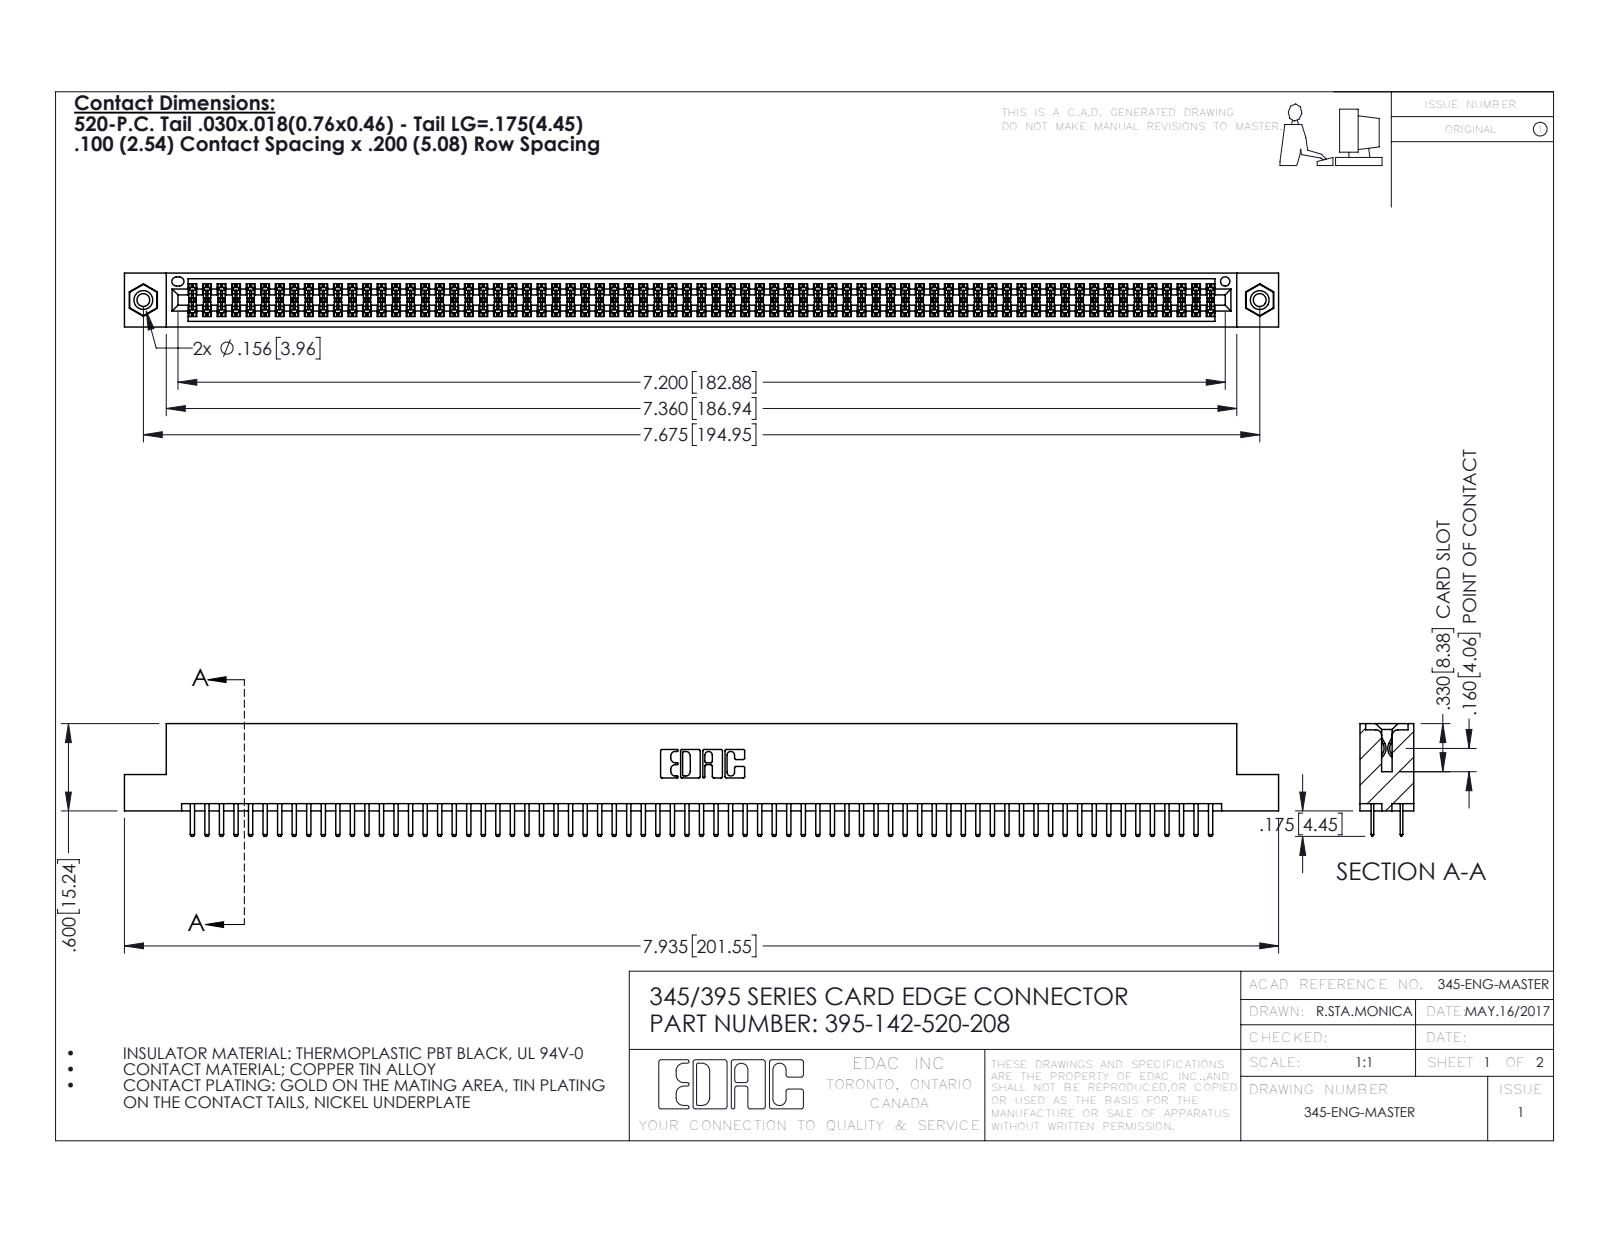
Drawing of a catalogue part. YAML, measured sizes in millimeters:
part_name: "345-292-001_345-293-120; 395-142-520-208; 345 Part_Flush Mounting Lugs - 0.156 Dia-TI; 345-250-001_345-250-003-102"
step_written_by: "SolidWorks 2016 (CONFIG_CONTROL_DESIGN)"
units: millimeters
bodies: {solids: 145, faces: 7854, planar: 5082, cylindrical: 2756, other: 16}
overall_size: [201.5, 19.7, 9.4]
volume: 19780
surface_area: 29680
round_holes:
  - {diameter: 2.3, count: 2}
  - {diameter: 3.2, count: 2}
  - {diameter: 4, count: 2}
  - {diameter: 1.6, count: 1}
round_bosses_or_shafts:
  - {diameter: 3.9, count: 2}
partial_cylinders:
  - {radius: 0.2, count: 213}
  - {radius: 0.3, count: 146}
  - {radius: 0.3, count: 22}
  - {radius: 0.2, count: 6}
  - {radius: 0.8, count: 6}
  - {radius: 0.7, count: 3}
  - {radius: 0.4, count: 2}
  - {radius: 0.5, count: 2}
face_to_face_distances: [1.8, 7.6, 5.1, 9.4, 2.5, 6.9, 0.6, 5.7, 0.6, 1.8]
hole_center_spacings: [6.9, 189, 194.9]
